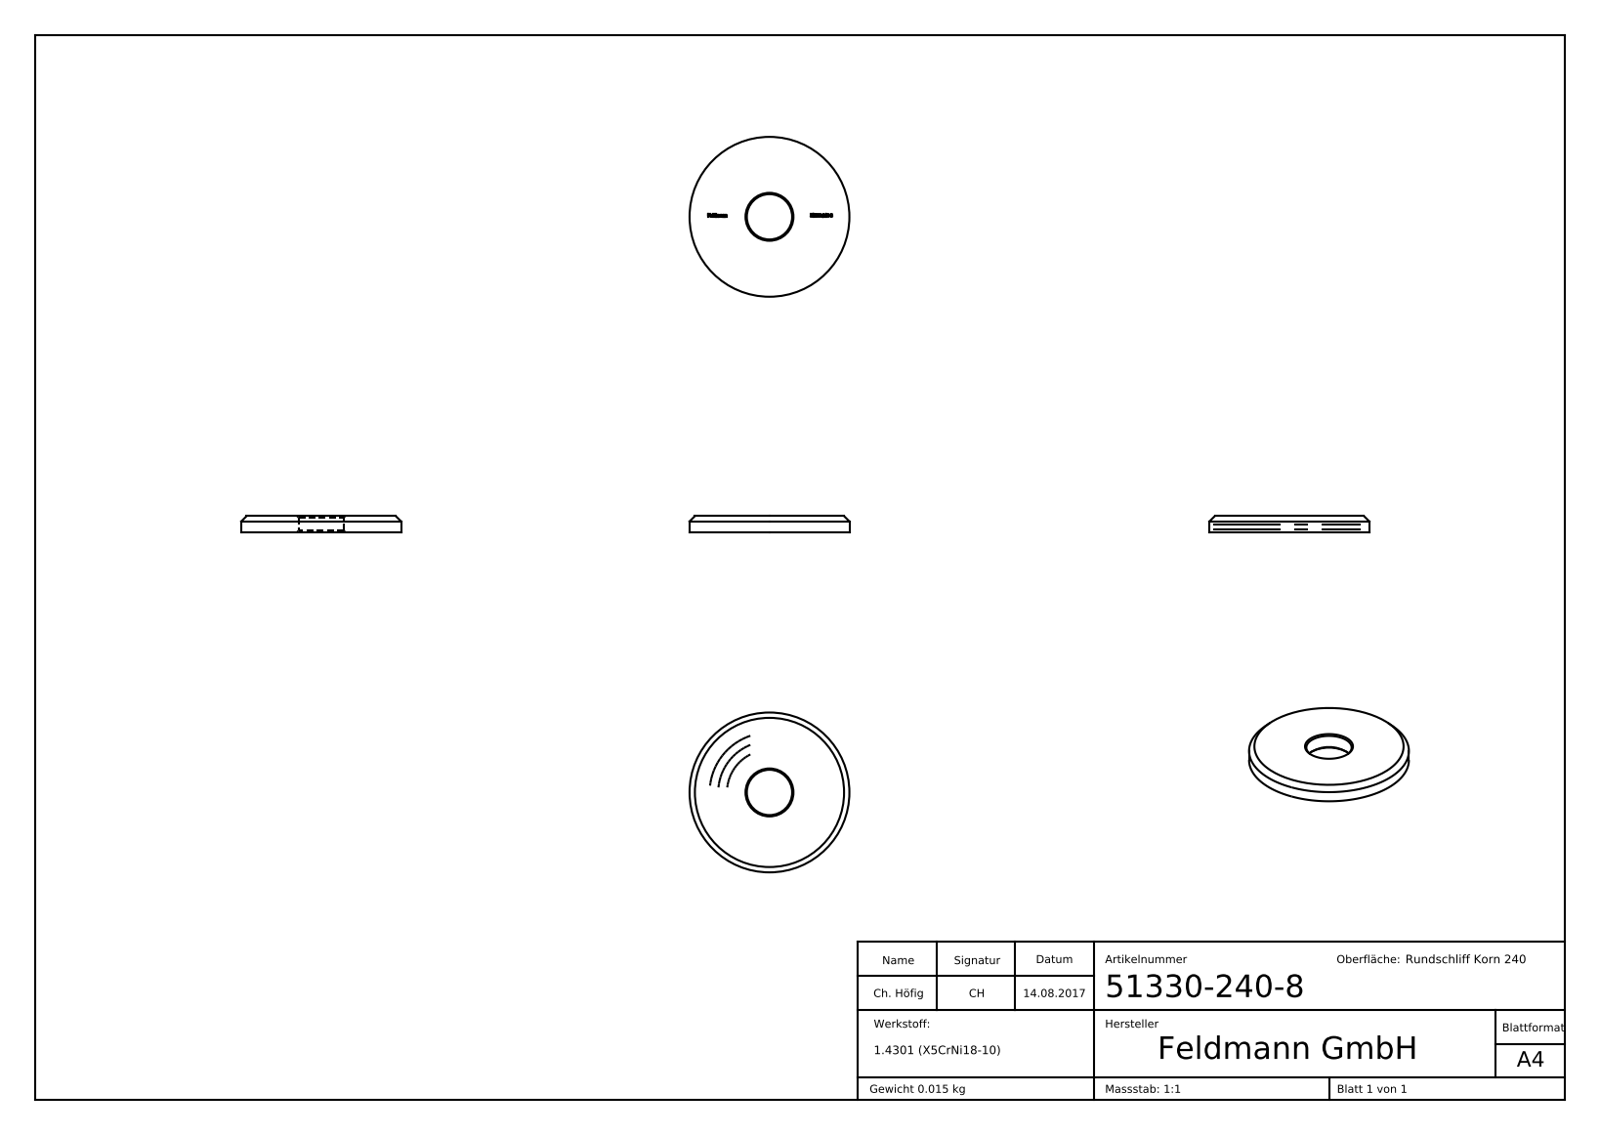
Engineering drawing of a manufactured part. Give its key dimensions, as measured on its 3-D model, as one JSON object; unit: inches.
{"part_name": "51330-240-8", "step_written_by": "SolidWorks 2018 (CONFIG_CONTROL_DESIGN)", "units": "inches", "bodies": {"solids": 1, "faces": 263, "planar": 128, "cylindrical": 4, "other": 131}, "overall_size": [1.181, 1.181, 0.118], "volume_in3": 0.116, "surface_area_in2": 2.485, "round_holes": [[0.335, 1]], "round_bosses_or_shafts": [[1.181, 1]], "face_to_face_distances": [0.118, 0.114, 0.047, 0.026, 0.745, 0.021, 0.014, 0.838, 0.093, 0.022]}
